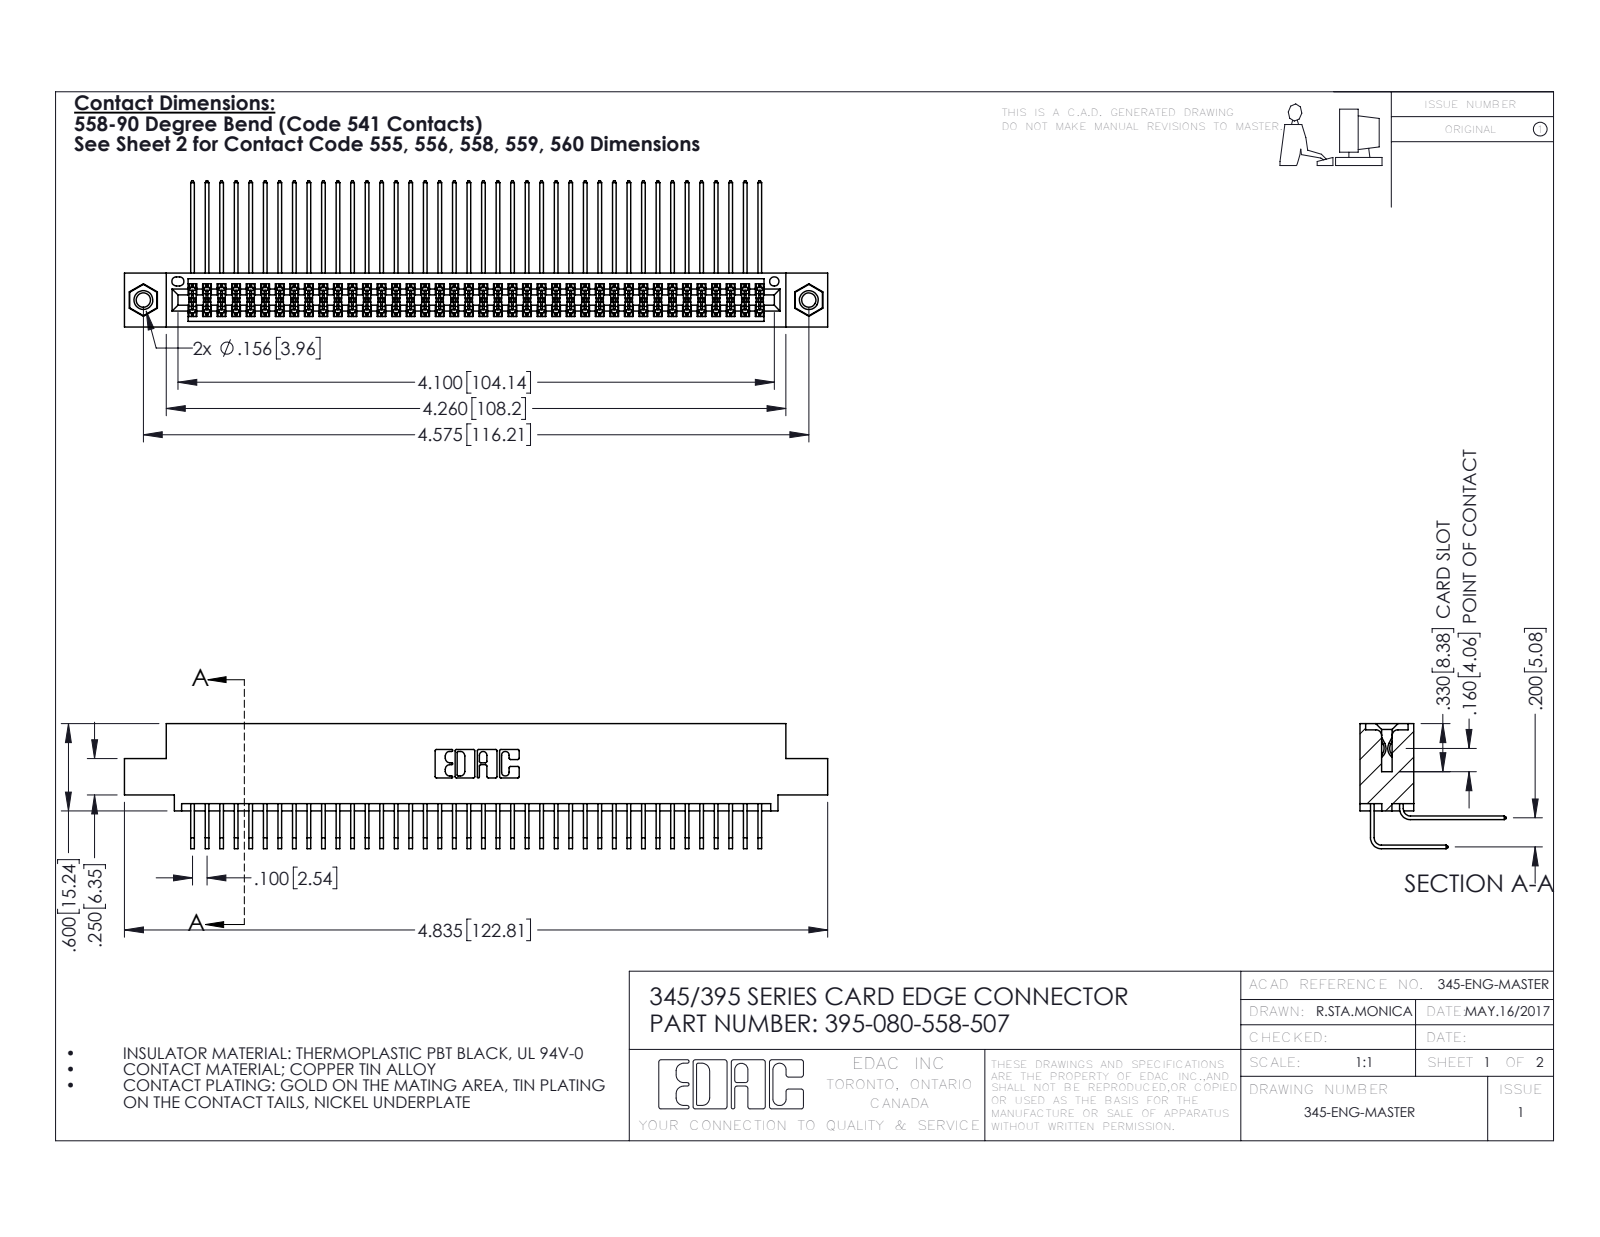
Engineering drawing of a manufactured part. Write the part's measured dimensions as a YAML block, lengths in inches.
part_name: "345-292-001_558 Tail - 2; 345-292-001_558 559 Tail - 1; 345-250-001_345-250-005-103; 345 Part_0.110 Offset - 0.156 Dia-TI (+1 more)"
step_written_by: "SolidWorks 2016 (CONFIG_CONTROL_DESIGN)"
units: inches
bodies: {solids: 83, faces: 4350, planar: 2916, cylindrical: 1418, other: 16}
overall_size: [4.835, 1.005, 0.859]
volume: 0.75
surface_area: 31.64
round_holes:
  - {diameter: 0.098, count: 2}
  - {diameter: 0.125, count: 2}
  - {diameter: 0.156, count: 2}
  - {diameter: 0.064, count: 1}
round_bosses_or_shafts:
  - {diameter: 0.155, count: 2}
partial_cylinders:
  - {radius: 0.006, count: 121}
  - {radius: 0.01, count: 22}
  - {radius: 0.007, count: 6}
  - {radius: 0.031, count: 6}
  - {radius: 0.026, count: 3}
  - {radius: 0.014, count: 2}
  - {radius: 0.019, count: 2}
  - {radius: 0.022, count: 2}
face_to_face_distances: [0.072, 0.298, 0.2, 0.37, 0.098, 0.272, 0.025, 0.225, 0.025, 0.175]
hole_center_spacings: [0.27, 4.339, 4.575]
